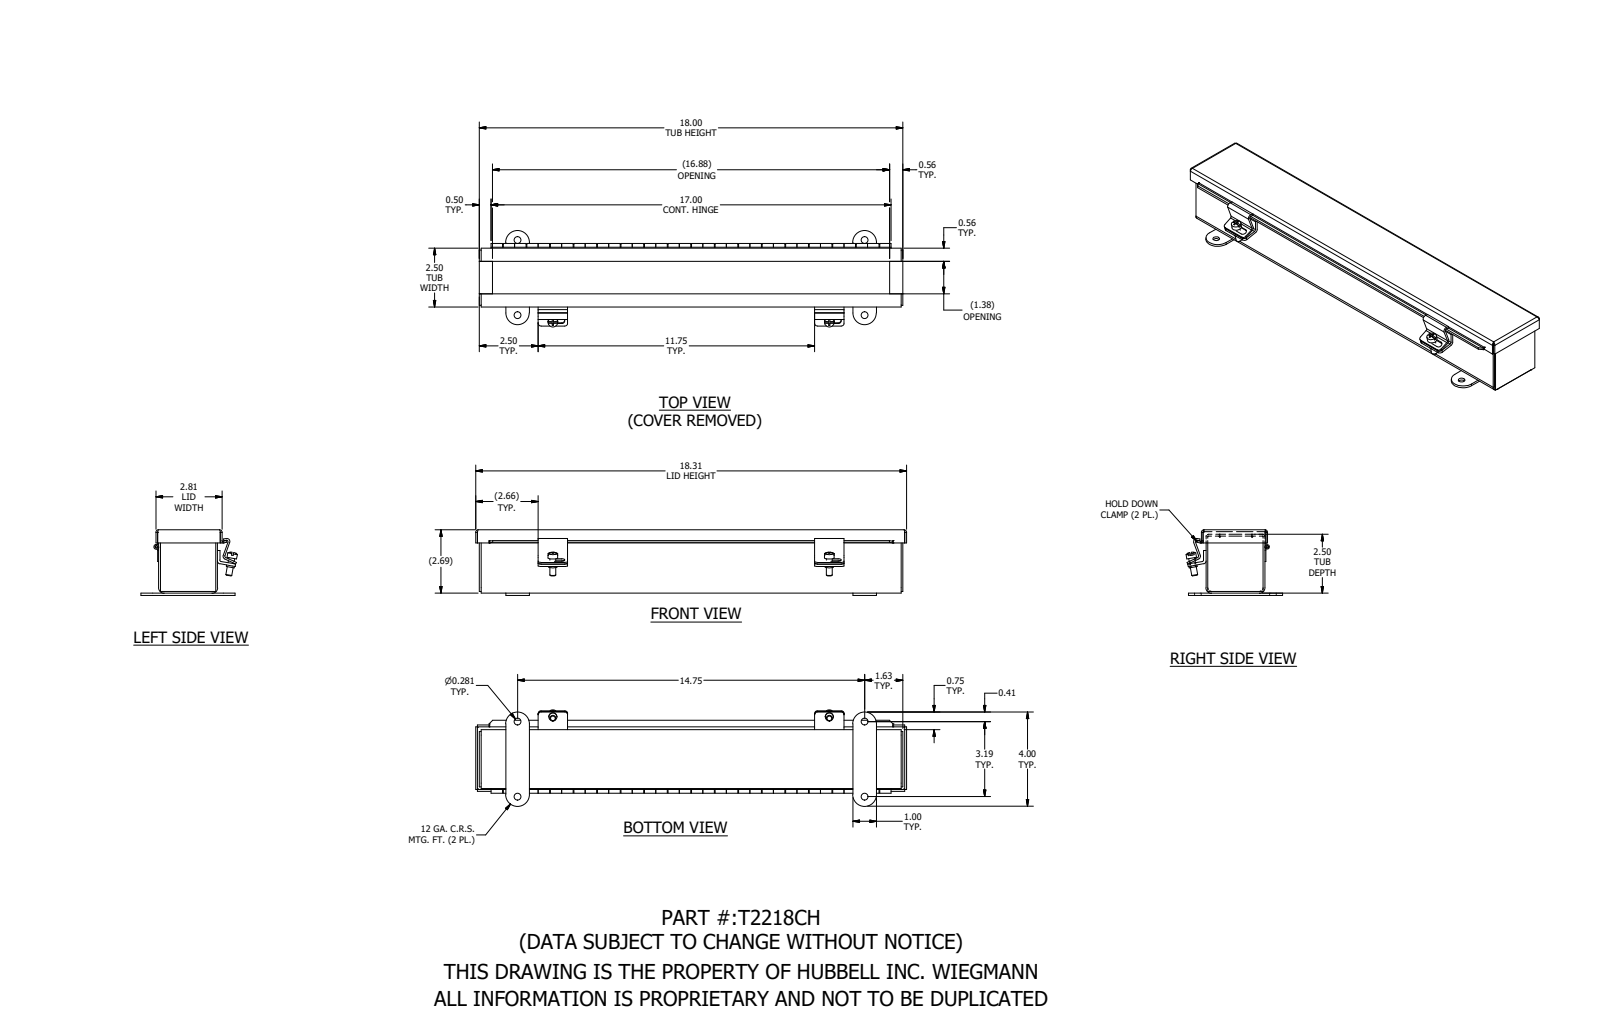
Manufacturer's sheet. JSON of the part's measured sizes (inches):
{"part_name": "T2218CH", "step_written_by": "SolidWorks 2021 (AUTOMOTIVE_DESIGN)", "units": "inches", "bodies": {"solids": 15, "faces": 504, "planar": 268, "cylindrical": 218, "other": 18}, "overall_size": [18.313, 4.095, 2.783], "volume_in3": 19.67, "surface_area_in2": 564.4, "round_holes": [[0.281, 4], [0.196, 2], [0.116, 1]], "round_bosses_or_shafts": [[0.41, 2], [0.344, 2], [0.25, 2], [0.2, 1], [0.1, 1]], "partial_cylinders_radius": [[0.031, 9], [0.105, 9], [0.125, 8], [0.133, 4], [0.5, 4], [0.063, 3], [0.126, 3], [0.156, 2]], "face_to_face_distances": [0.074, 2.426, 2.615, 2.5, 2.352, 2.689, 2.541, 0.189, 2.542, 0.116], "hole_center_spacings": [3.187, 14.75, 15.091, 11.75]}
